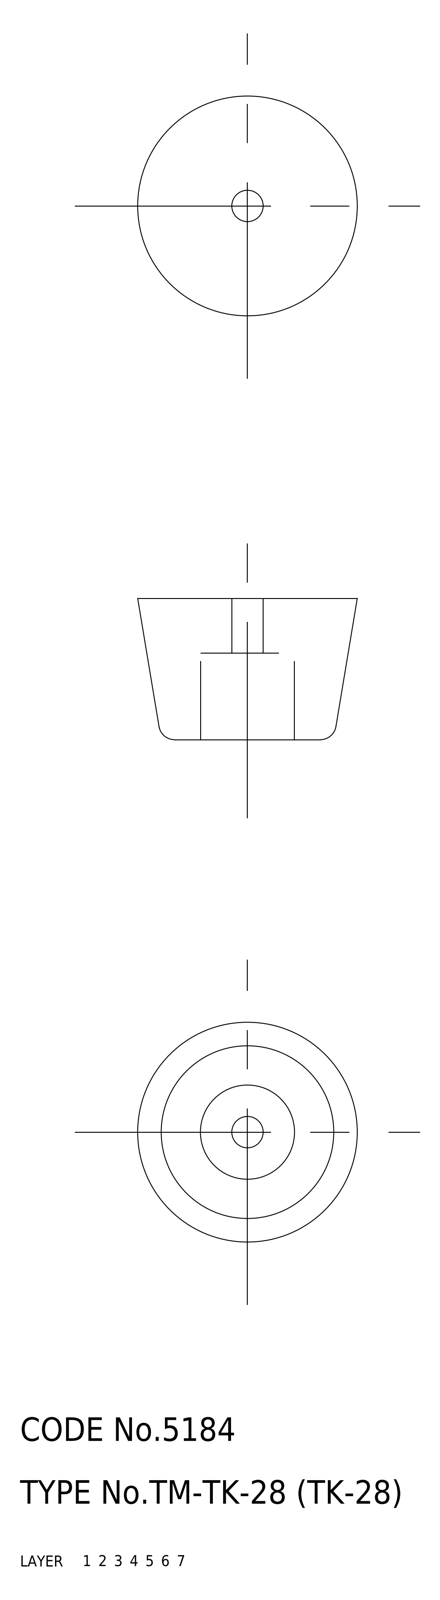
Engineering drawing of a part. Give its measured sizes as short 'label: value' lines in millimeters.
name: washer; rubber foot; TK_28_9559_36
written by: CADfix (AUTOMOTIVE_DESIGN)
unit: mm
bodies: 2 solids, 20 faces (0 planar, 0 cylindrical, 20 other)
size: 28 × 28 × 18
volume: 7 526 mm³; area: 3 319 mm²
